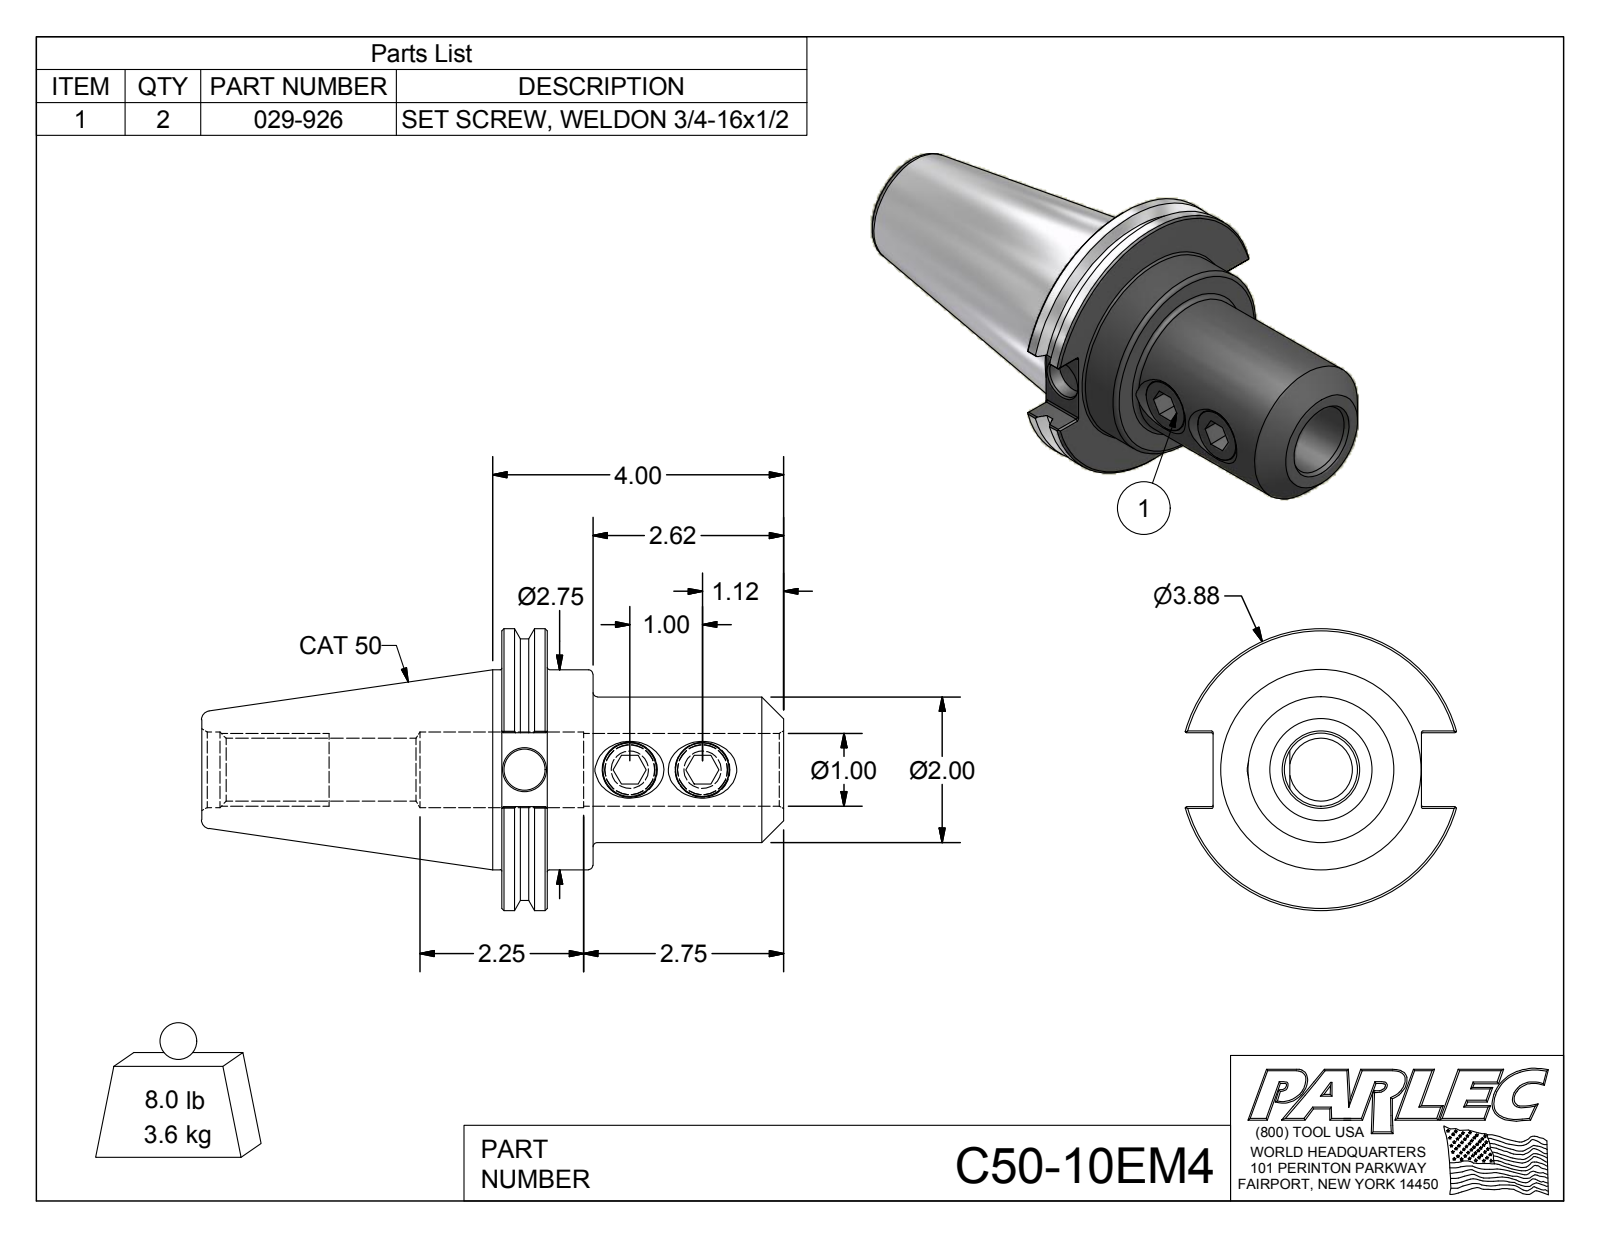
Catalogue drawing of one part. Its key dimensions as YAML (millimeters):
part_name: "C50-10EM4; C50-10EM4-1; 029-926"
step_written_by: "Autodesk Inventor 2012 (AUTOMOTIVE_DESIGN)"
units: millimeters
bodies: {solids: 3, faces: 122, planar: 51, cylindrical: 33, other: 38}
overall_size: [203.2, 98.4, 94.7]
volume: 454700
surface_area: 68260
round_holes:
  - {diameter: 17.4, count: 2}
  - {diameter: 8, count: 1}
  - {diameter: 10.1, count: 1}
  - {diameter: 22, count: 1}
  - {diameter: 25.4, count: 1}
  - {diameter: 26.4, count: 1}
  - {diameter: 26.4, count: 1}
round_bosses_or_shafts:
  - {diameter: 19.1, count: 2}
  - {diameter: 98.4, count: 1}
  - {diameter: 91.3, count: 1}
  - {diameter: 69.9, count: 1}
  - {diameter: 69.3, count: 1}
  - {diameter: 50.8, count: 1}
partial_cylinders:
  - {radius: 0.5, count: 12}
face_to_face_distances: [15.9, 31.9, 16, 22, 10, 98.4, 82.6, 66.5, 104.8, 120.7]
hole_center_spacings: [25.4, 36.7, 62.1]
